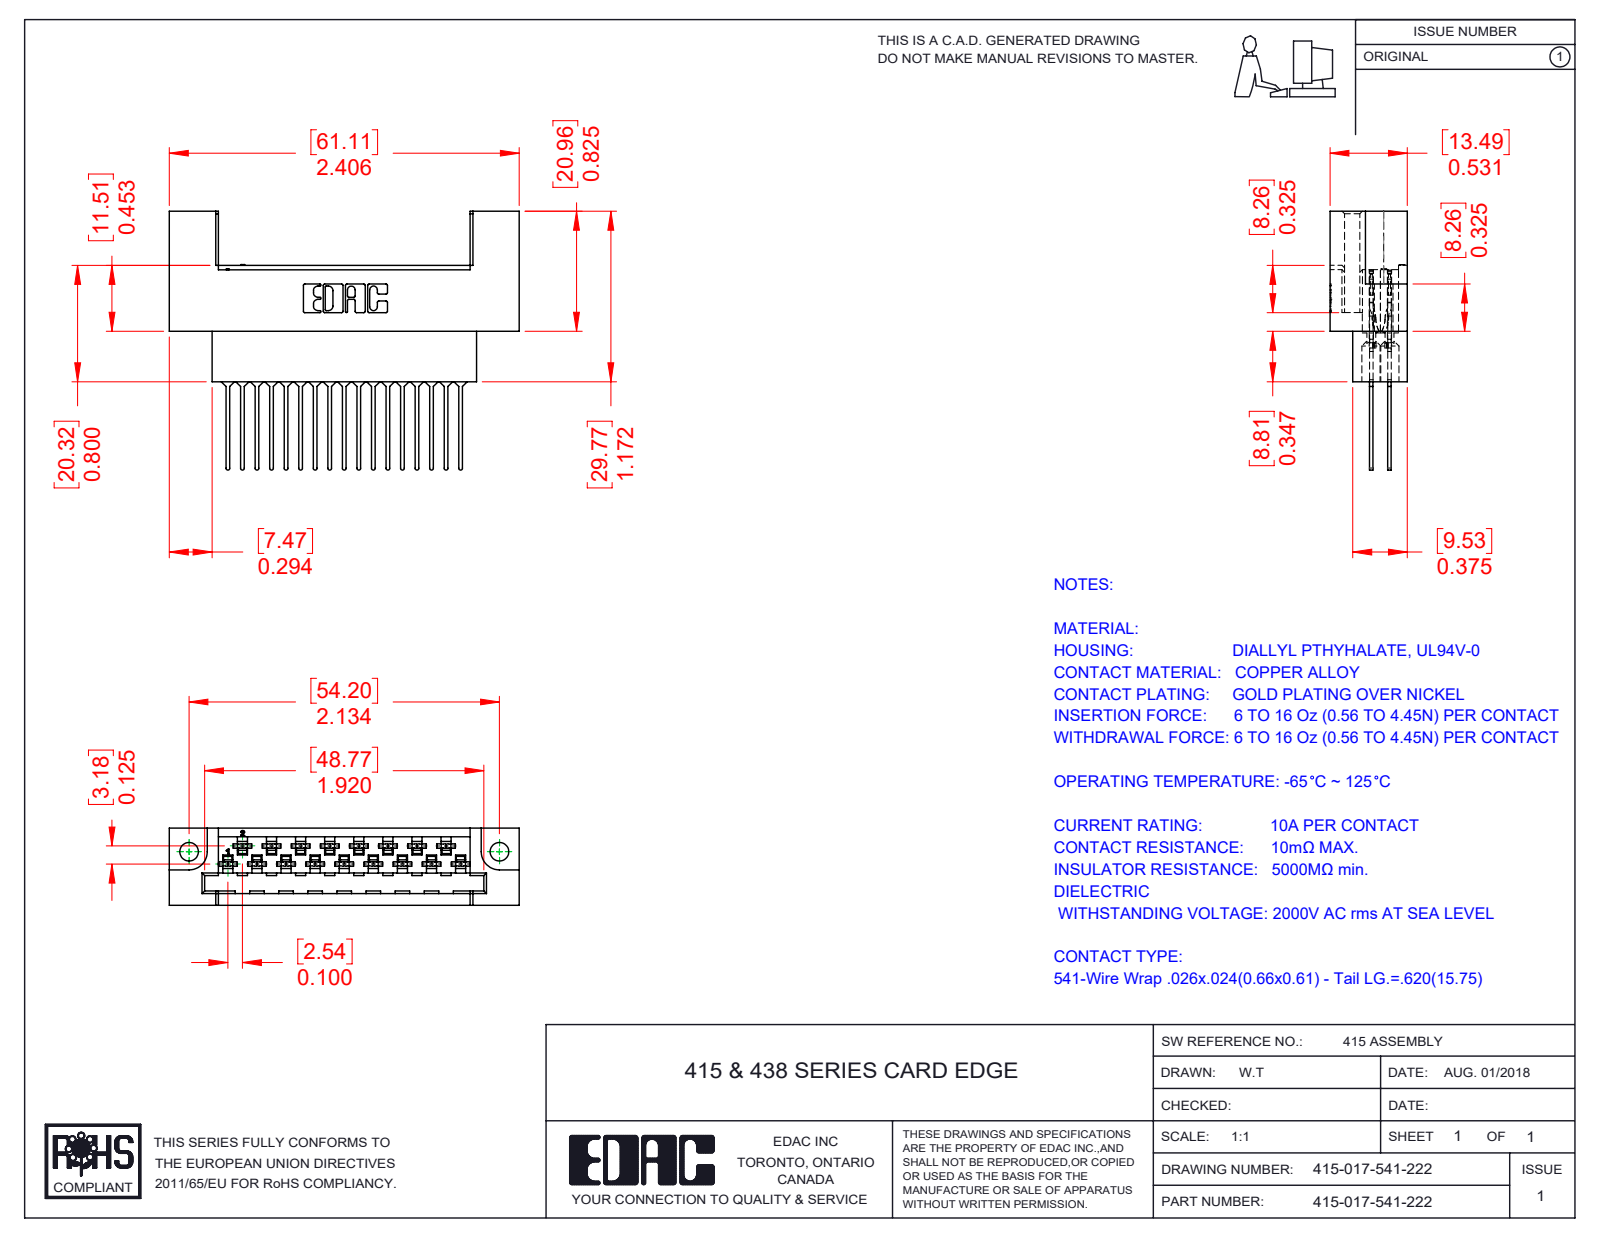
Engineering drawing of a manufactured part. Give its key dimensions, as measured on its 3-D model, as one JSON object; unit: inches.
{"part_name": "415-017-541-222; 415-210-001_415-210-017-222; 516-290-001_541", "step_written_by": "SolidWorks 2016 (CONFIG_CONTROL_DESIGN)", "units": "inches", "bodies": {"solids": 18, "faces": 1826, "planar": 1163, "cylindrical": 488, "other": 175}, "overall_size": [2.406, 1.778, 0.531], "volume_in3": 0.662, "surface_area_in2": 20.05, "round_holes": [[0.05, 17], [0.13, 17], [0.128, 2]], "partial_cylinders_radius": [[0.012, 68], [0.022, 68], [0.007, 34], [0.008, 34], [0.016, 34], [0.08, 34], [0.01, 22], [0.013, 17]], "face_to_face_distances": [0.125, 0.024, 0.531, 0.295, 0.05, 0.074, 0.26, 0.271, 0.236, 0.111], "hole_center_spacings": [0.2, 0.4, 0.6, 0.8, 0.1, 0.16, 0.3, 0.325]}
